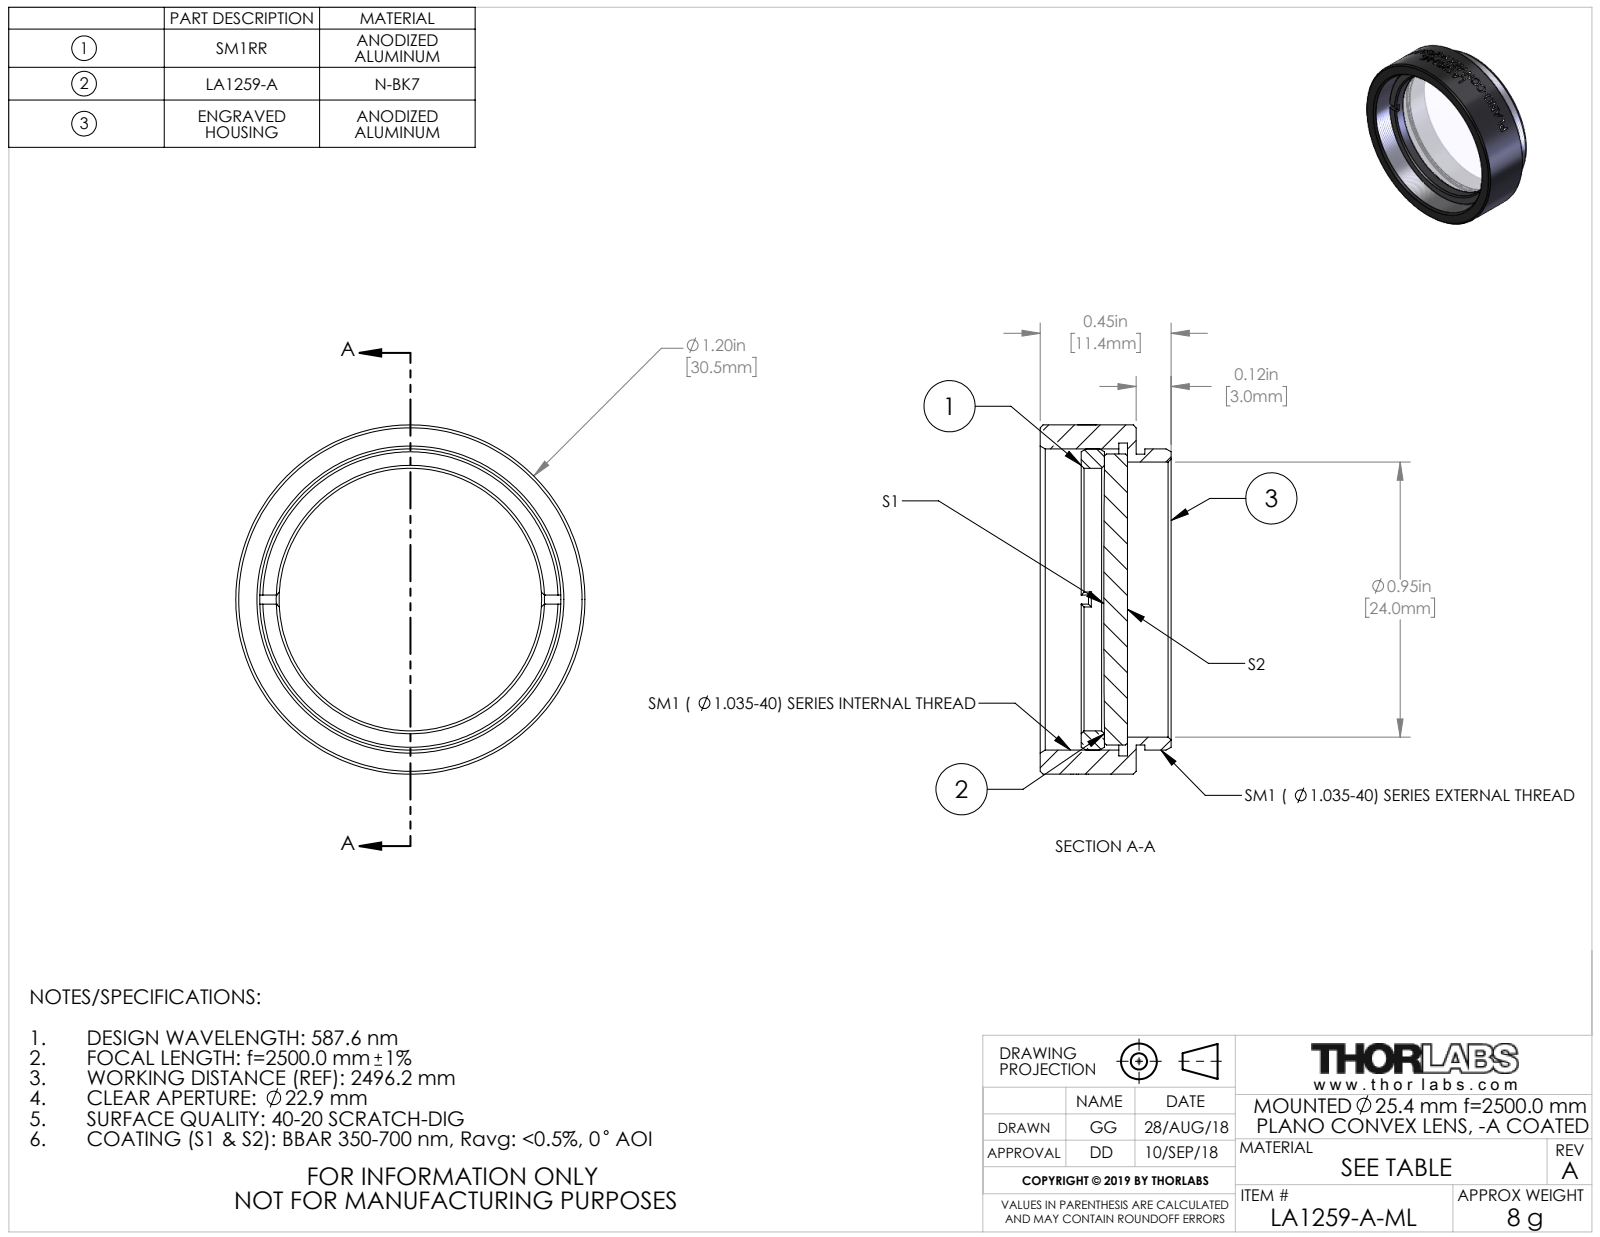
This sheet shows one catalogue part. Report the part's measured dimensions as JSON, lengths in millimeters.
{"part_name": "TTN162144-E0W", "step_written_by": "SolidWorks 2018 (CONFIG_CONTROL_DESIGN)", "units": "millimeters", "bodies": {"solids": 3, "faces": 138, "planar": 20, "cylindrical": 90, "other": 28}, "overall_size": [30.48, 30.48, 11.43], "volume_mm3": 3107, "surface_area_mm2": 4296, "round_holes": [[22.91, 1], [24, 1], [27.3, 1]], "round_bosses_or_shafts": [[30.48, 1], [26.29, 1], [25.4, 1], [25.37, 1]], "face_to_face_distances": [0.77, 8.39, 7.62, 2.77, 2, 5.62, 4.8, 4.03, 2.03, 3.59]}
